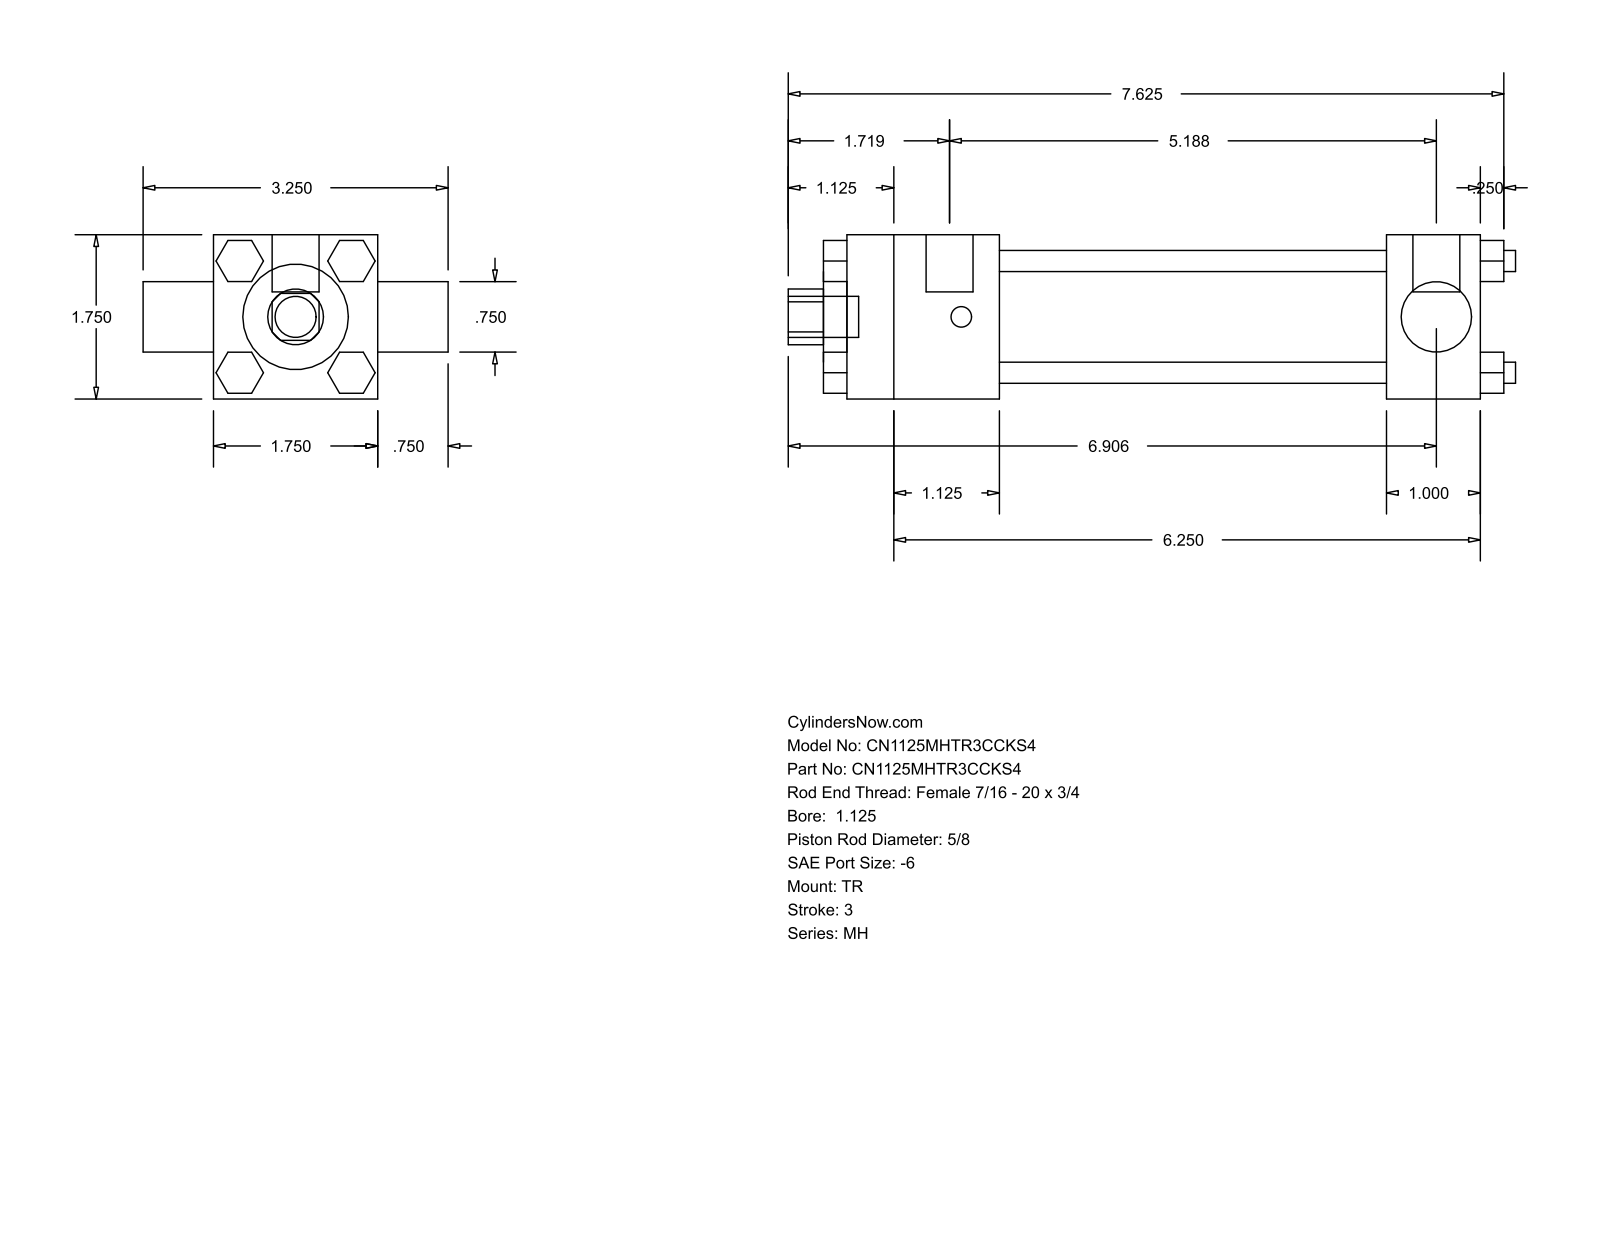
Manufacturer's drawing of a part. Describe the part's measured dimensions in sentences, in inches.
The part is named "MH_TR__0112_0.625". Its 3-D file was written by "GSSL Pune (CONFIG_CONTROL_DESIGN)". It is 0 solids with 120 faces: 92 planar, 28 cylindrical and 0 other. Overall it measures 7.75 by 3.25 by 1.75 inches. Round holes: 1 of diameter 0.625, 1 of diameter 0.75, 1 of diameter 1.125, 1 of diameter 1.375. Round bosses or shafts: 4 of diameter 0.225, 3 of diameter 0.219, 2 of diameter 0.5, 1 of diameter 0.437. Partial cylindrical surfaces (rounded edges, fillets, slot ends): 1 of radius 0.297. The main face-to-face distances are 1.75, 0.437, 4.125, 5.125, 1, 1.625, 5.75, 6.75, 1.875, 0.25.
